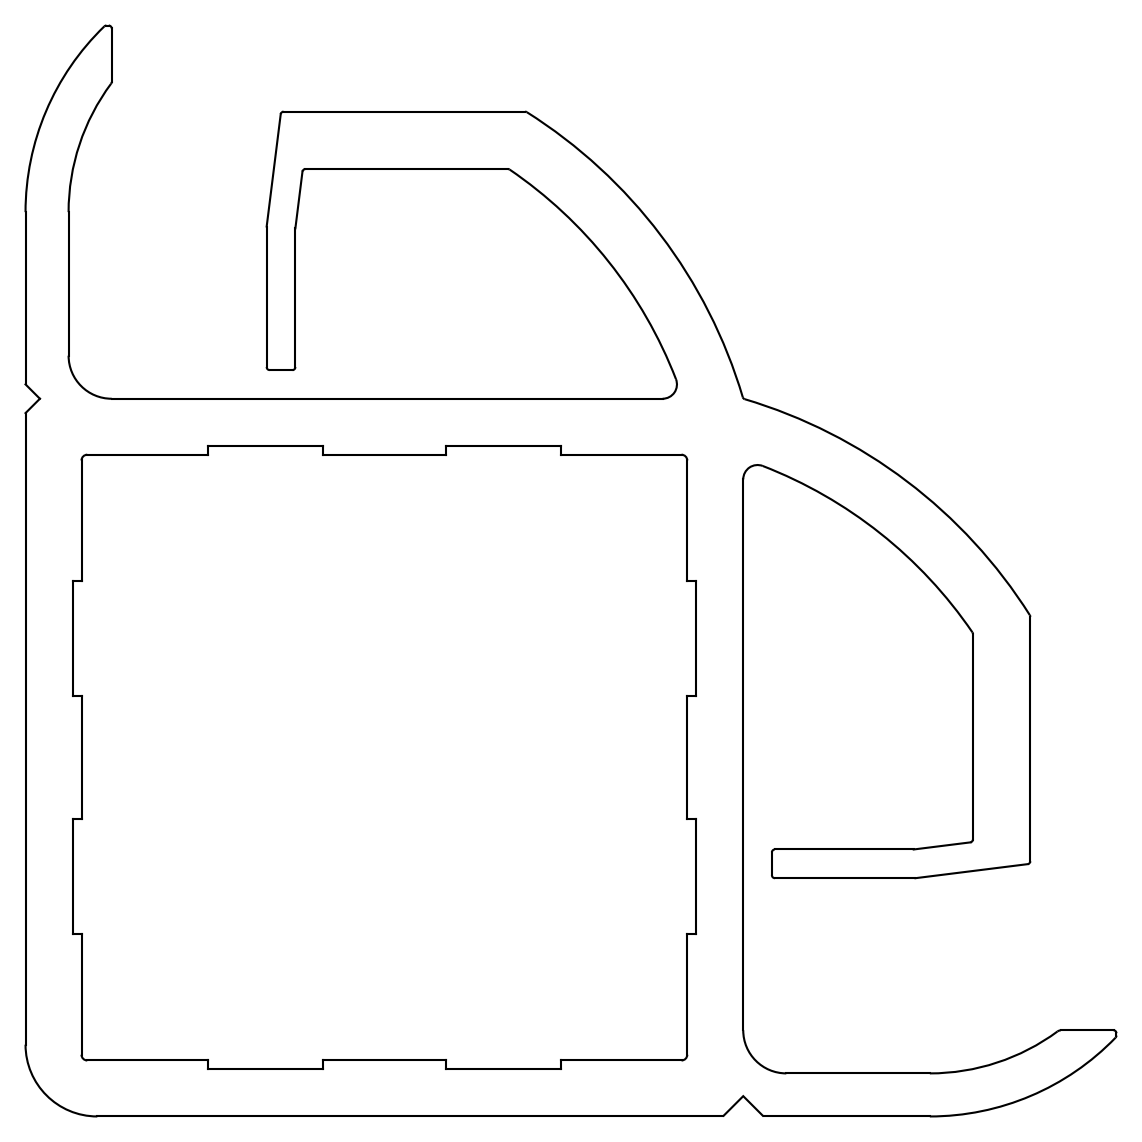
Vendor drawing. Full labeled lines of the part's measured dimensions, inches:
STEP written by: THINKDESIGN (CONFIG_CONTROL_DESIGN)
Units: inches
Bodies: 1 solid, 104 faces (68 planar, 36 cylindrical, 0 other)
Overall size (bounding box): 3.937 × 1.496 × 1.496
Volume: 1.838 in³ · Surface area: 54.47 in²
Partial cylindrical surfaces — rounded edges, fillets, slot ends (radius × count): R0.004 ×18, R0.008 ×5, R0.02 ×2, R0.059 ×2, R0.295 ×2, R0.354 ×2, R0.619 ×2, R0.698 ×2
Main face-to-face distances: 0.077, 0.907, 0.984, 0.919, 0.065, 0.843, 0.831, 0.459, 1.378, 1.301
